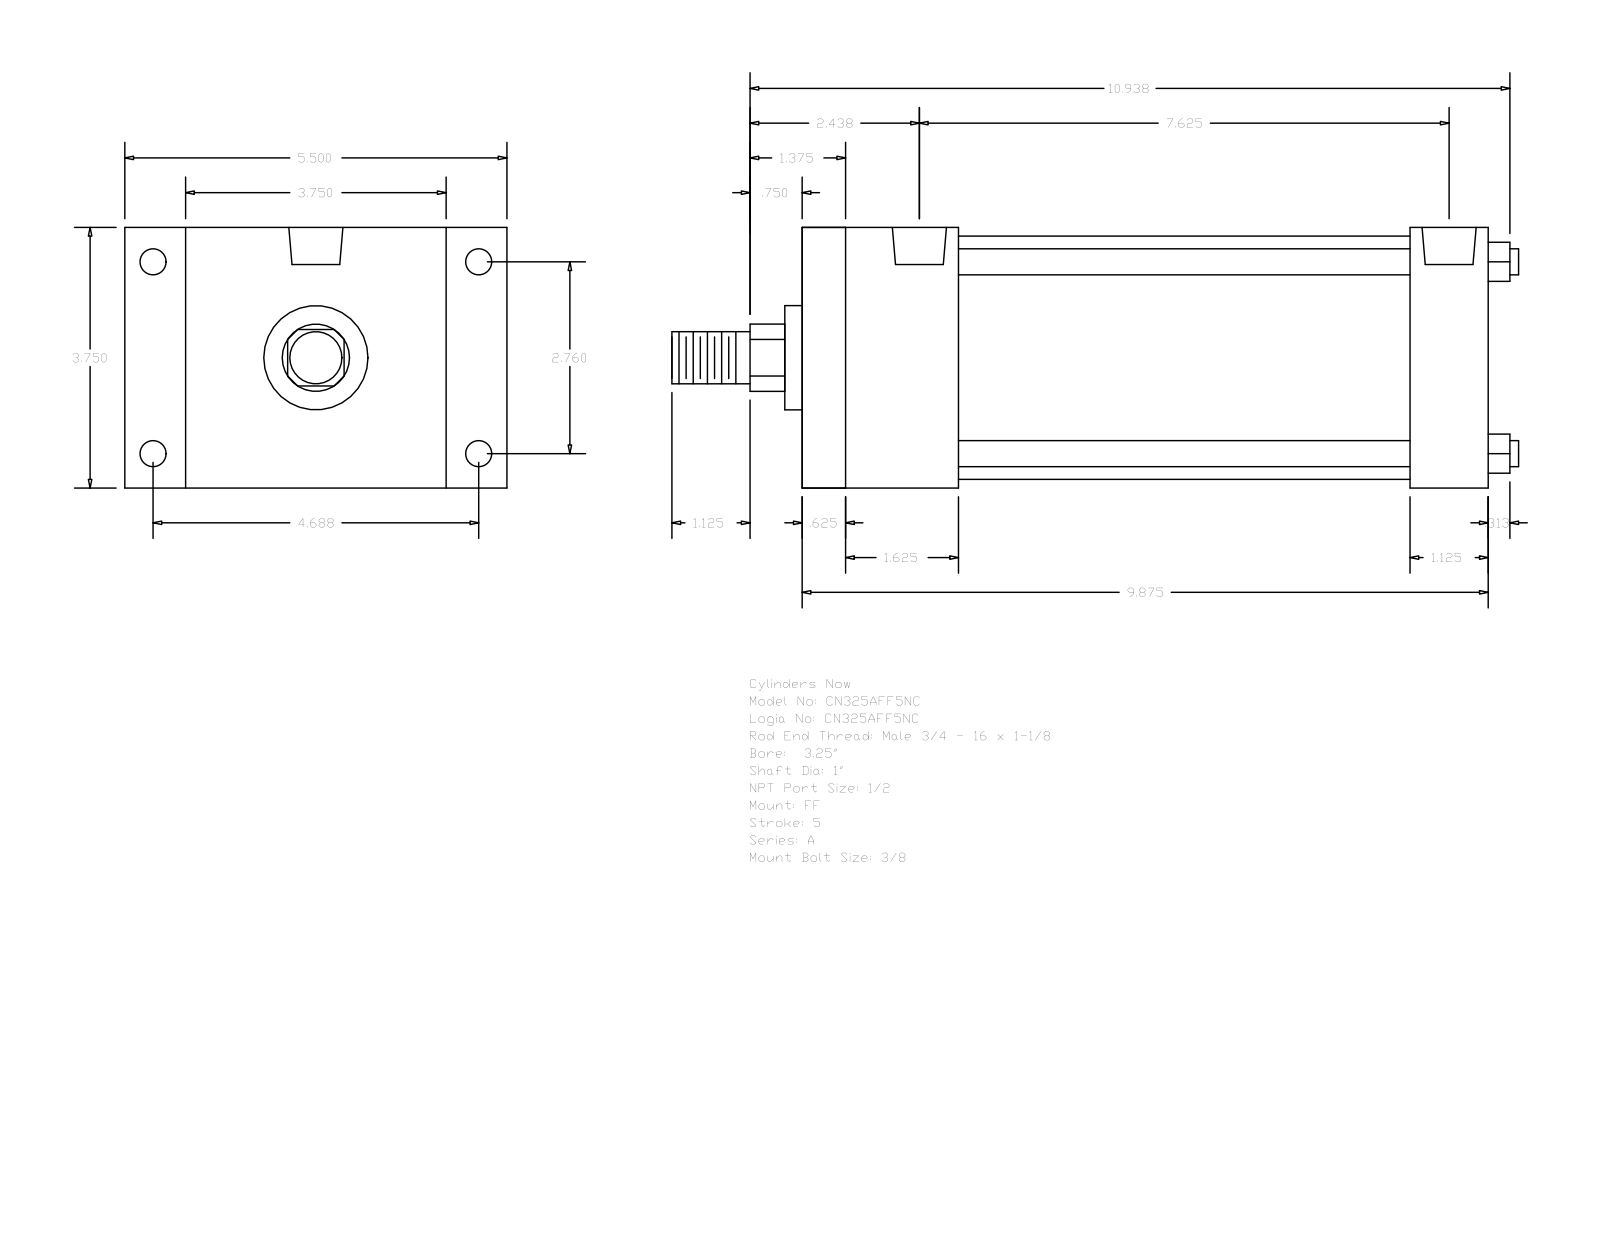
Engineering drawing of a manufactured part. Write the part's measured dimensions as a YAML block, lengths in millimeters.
part_name: "A_FF__0325_1"
step_written_by: "GSSL Pune (CONFIG_CONTROL_DESIGN)"
units: millimeters
bodies: {solids: 0, faces: 92, planar: 64, cylindrical: 28, other: 0}
overall_size: [309.56, 139.7, 95.25]
round_holes:
  - {diameter: 8.73, count: 4}
  - {diameter: 9.53, count: 4}
  - {diameter: 19.77, count: 2}
round_bosses_or_shafts:
  - {diameter: 9.53, count: 4}
  - {diameter: 88.9, count: 1}
  - {diameter: 38.1, count: 1}
  - {diameter: 25.4, count: 1}
  - {diameter: 19.05, count: 1}
partial_cylinders:
  - {radius: 12.29, count: 1}
face_to_face_distances: [95.24, 250.83, 15.87, 234.96, 22.23, 117.47, 57.15, 222.25, 41.28, 206.38]
hole_center_spacings: [3.18, 70.1, 119.06, 138.16, 187.32, 190.5, 193.68]
